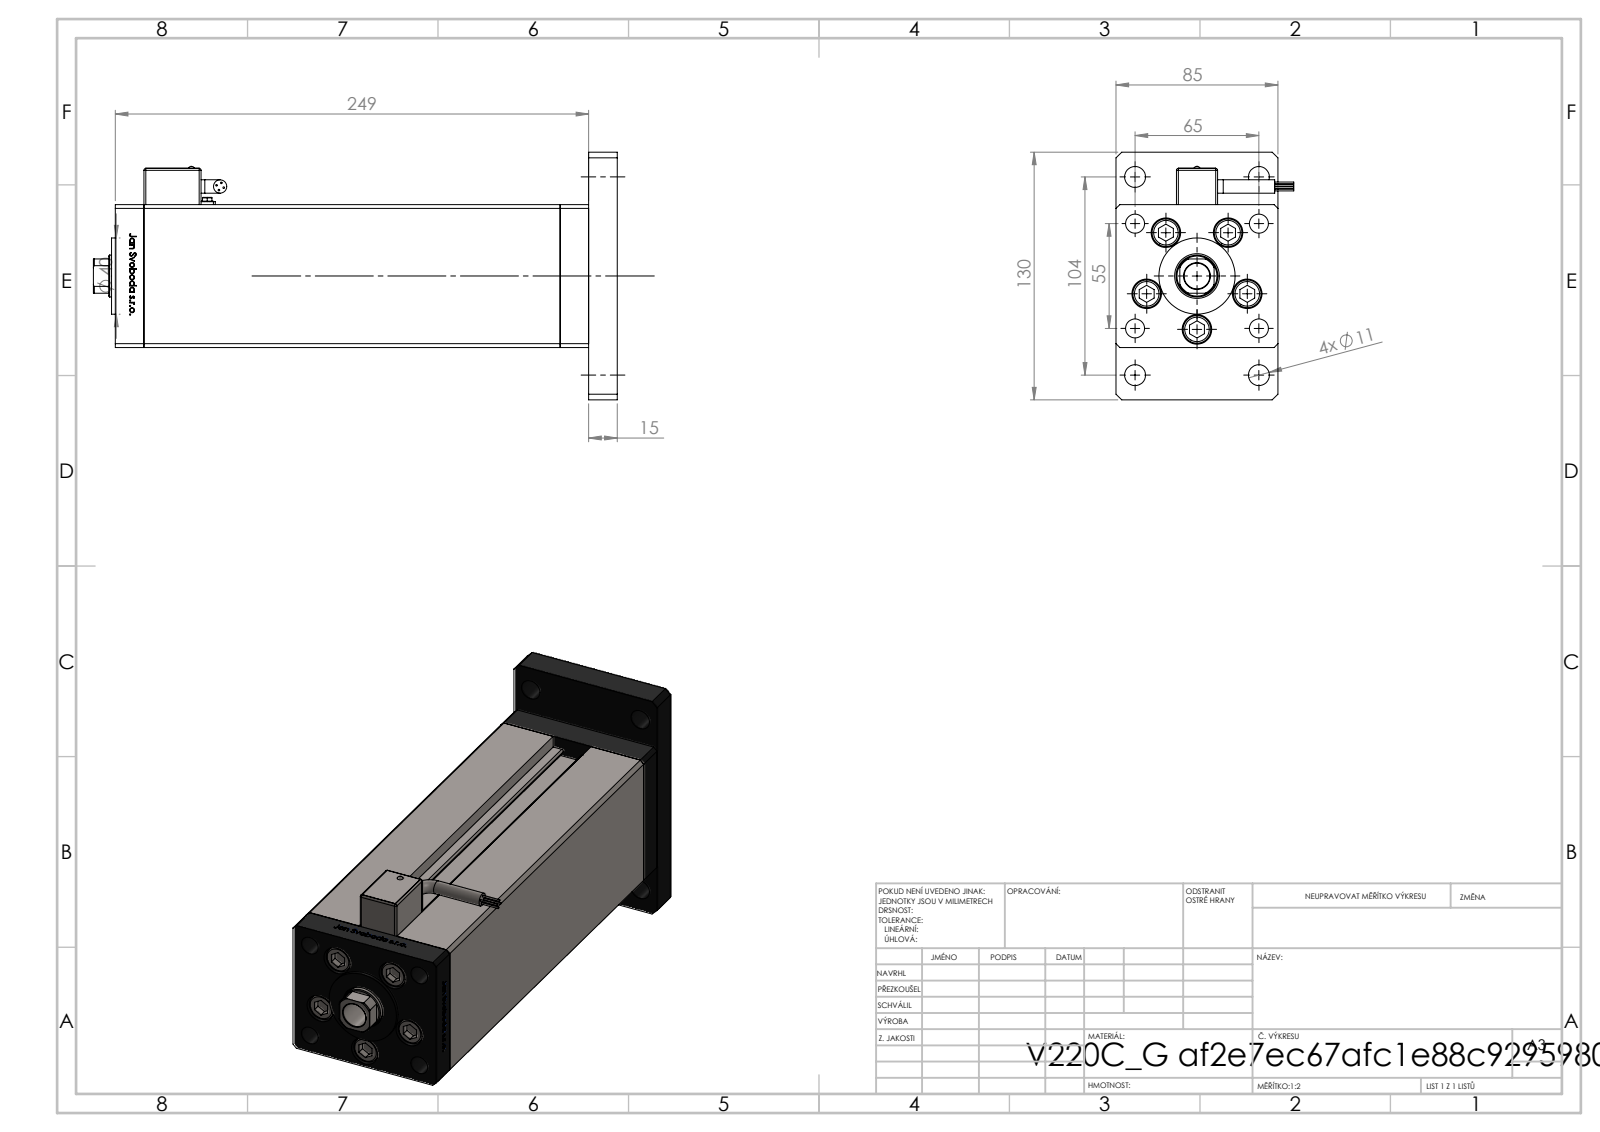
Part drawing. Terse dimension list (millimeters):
name: ALLEN BOLT; V220C_F; V220C_FRONT_G; Magnetic_Switch_MSU4 (+3 more)
written by: SolidWorks 2019 (CONFIG_CONTROL_DESIGN)
unit: mm
bodies: 20 solids, 1403 faces (553 planar, 226 cylindrical, 624 other)
size: 275 × 130 × 93.3
volume: 1 551 000 mm³; area: 239 368 mm²
holes: 9× ⌀10, 9× ⌀11, 5× ⌀15.5, 4× ⌀14.5, 1× ⌀3.6, 1× ⌀5, 1× ⌀7, 1× ⌀13.5, 1× ⌀22, 1× ⌀23.5, 1× ⌀56
bosses: 9× ⌀8, 5× ⌀14.5, 4× ⌀0.85, 2× ⌀7, 1× ⌀40, 1× ⌀6, 1× ⌀3.5, 1× ⌀2.5
rounds: 14× R1, 2× R0.93, 2× R4, 1× R10.5
face distances: 15, 85, 75, 233.5, 248.5, 218.5, 30, 2, 246.5, 263.5
hole spacings: 28, 24.5, 42.57, 61.32, 65, 69.46, 79.5, 102.69
